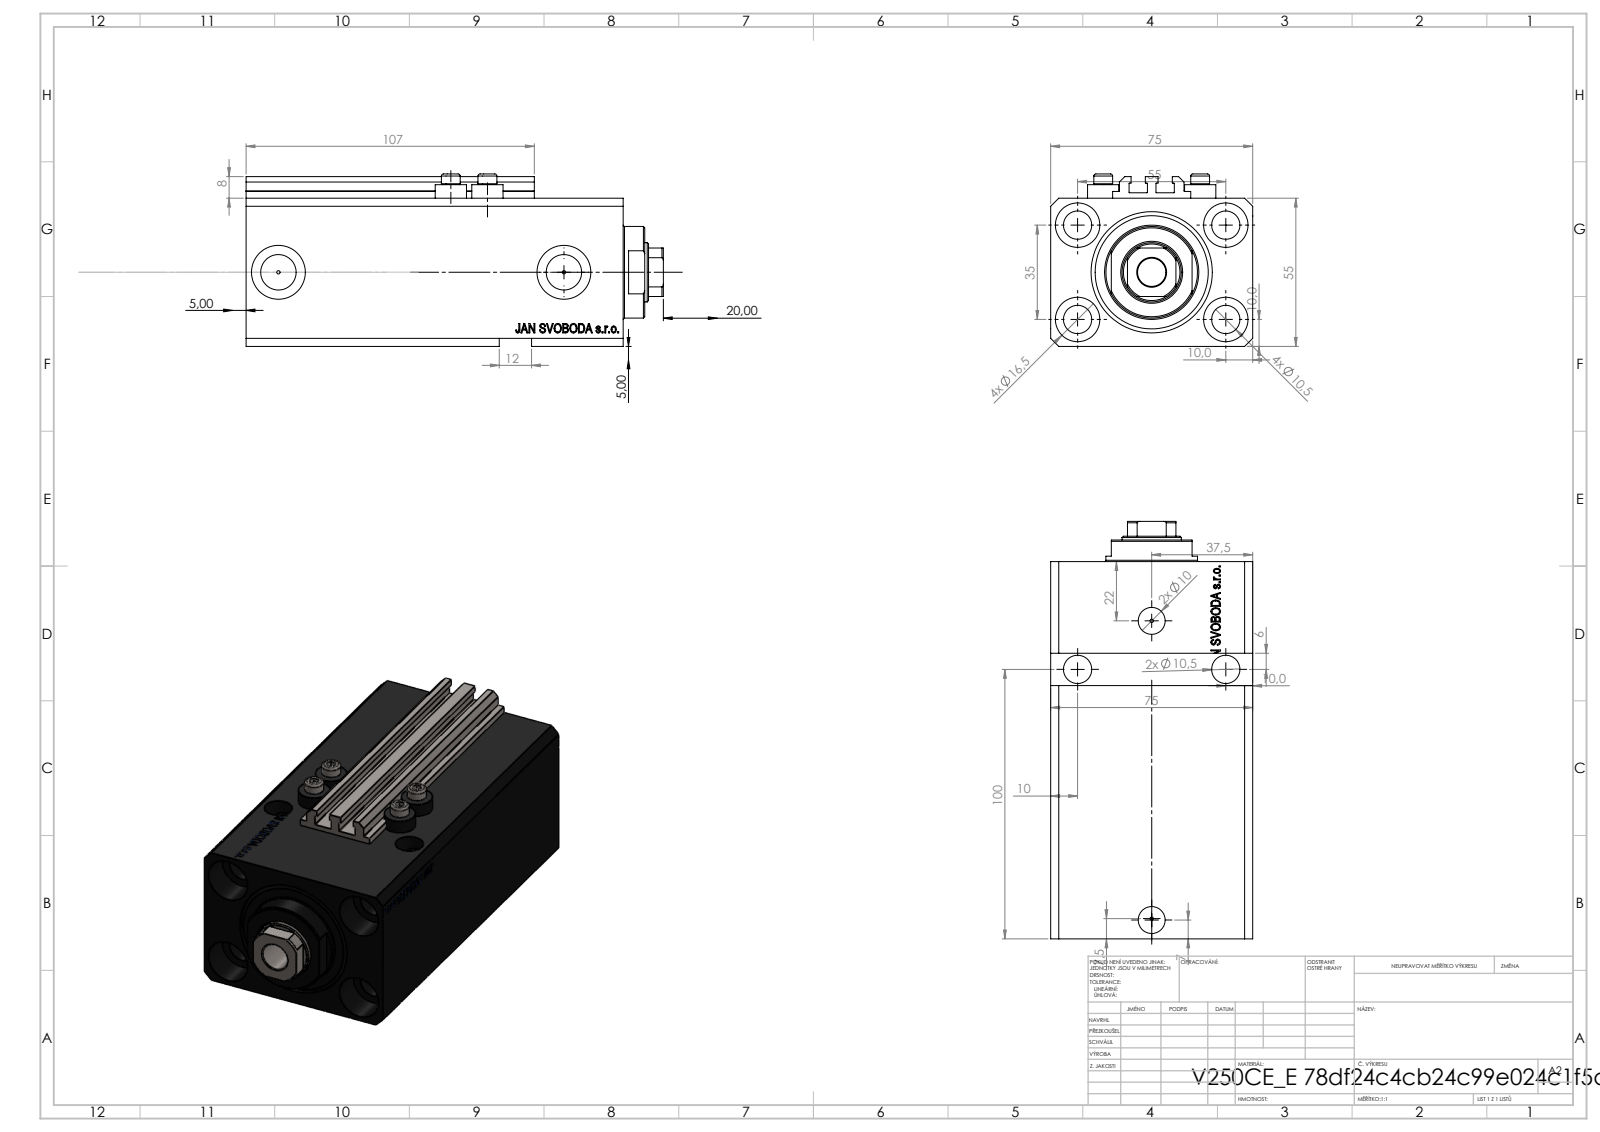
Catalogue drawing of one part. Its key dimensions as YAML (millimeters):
part_name: "V250CE_C_VCP; V250CE_VC_E; ALLEN BOLT V250CE; V250CE_E_Body"
step_written_by: "SolidWorks 2019 (CONFIG_CONTROL_DESIGN)"
units: millimeters
bodies: {solids: 8, faces: 1084, planar: 514, cylindrical: 146, other: 424}
overall_size: [155, 75, 64]
volume: 485219
surface_area: 115303
round_holes:
  - {diameter: 10.5, count: 9}
  - {diameter: 1.25, count: 4}
  - {diameter: 4, count: 4}
  - {diameter: 16.5, count: 4}
  - {diameter: 10, count: 2}
  - {diameter: 13.16, count: 2}
  - {diameter: 20, count: 2}
  - {diameter: 22, count: 1}
  - {diameter: 32, count: 1}
  - {diameter: 45, count: 1}
round_bosses_or_shafts:
  - {diameter: 11.6, count: 4}
  - {diameter: 7, count: 4}
  - {diameter: 34, count: 1}
partial_cylinders:
  - {radius: 0.2, count: 10}
  - {radius: 10.5, count: 1}
face_to_face_distances: [55, 75, 15, 140, 125, 3, 9.9, 57, 115.1, 130.1]
hole_center_spacings: [32.6, 32.87, 55, 96.98, 13.6, 14.09, 25.81, 32.58]
